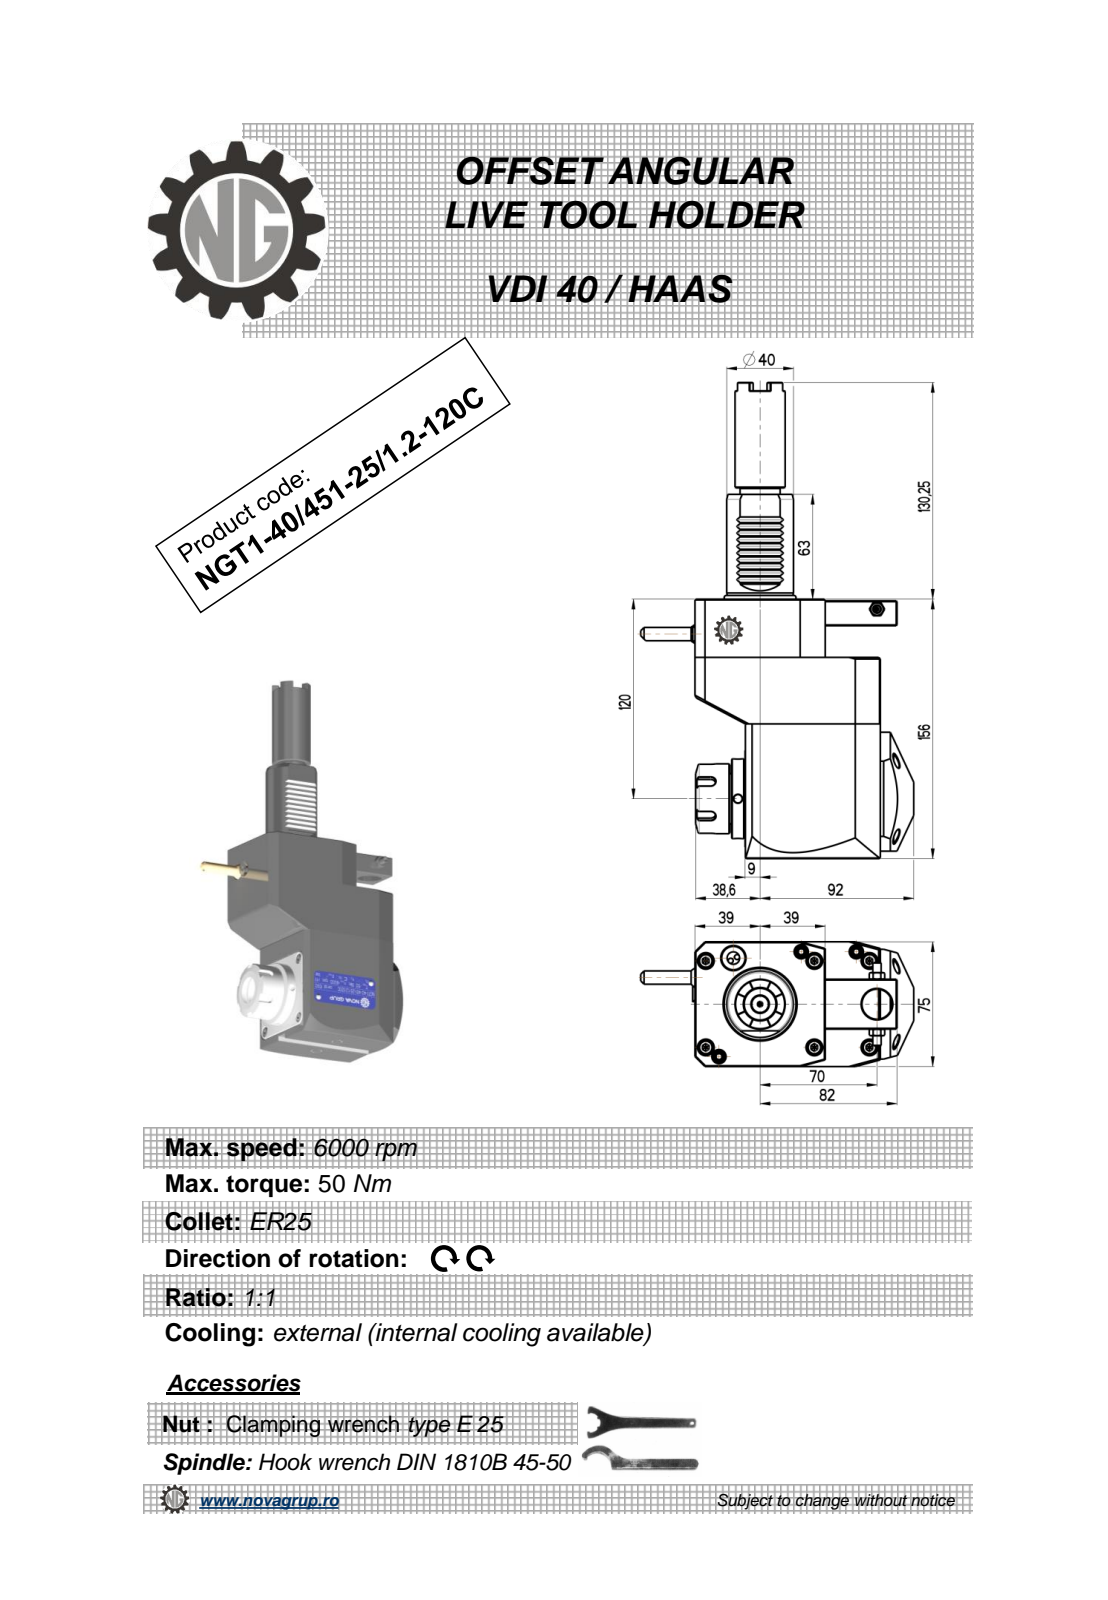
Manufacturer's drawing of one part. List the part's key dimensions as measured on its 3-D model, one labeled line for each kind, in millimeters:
Part name (STEP PRODUCT): NGT1_40_451_25_1_2_120C
STEP written by: PRO/ENGINEER BY PARAMETRIC TECHNOLOGY CORPORATION, 2010280 (CONFIG_CONTROL_DESIGN)
Units: millimetres
Bodies: 1 solid, 493 faces (235 planar, 95 cylindrical, 163 other)
Overall size (bounding box): 286.25 × 163.5 × 76.6
Volume: 1 219 000 mm³ · Surface area: 96 151 mm²
Round holes (diameter × count): ⌀5 ×3, ⌀3 ×1, ⌀4.2 ×1, ⌀9.5 ×1, ⌀18 ×1, ⌀19.5 ×1, ⌀20.3 ×1, ⌀26.8 ×1
Round bosses / shafts (diameter × count): ⌀48 ×1, ⌀42 ×1, ⌀40 ×1, ⌀37.5 ×1, ⌀33 ×1, ⌀30 ×1, ⌀26.58 ×1, ⌀24 ×1
Partial cylindrical surfaces — rounded edges, fillets, slot ends (radius × count): R0.26 ×12, R0.3 ×10, R0.2 ×6, R3 ×5, R0.5 ×1, R40 ×1
Main face-to-face distances: 75, 156, 111, 30, 121, 35, 81, 48, 33, 78
Hole centre spacings: 13.25, 20.93, 70, 83.25, 100.28, 112.5, 141.16
